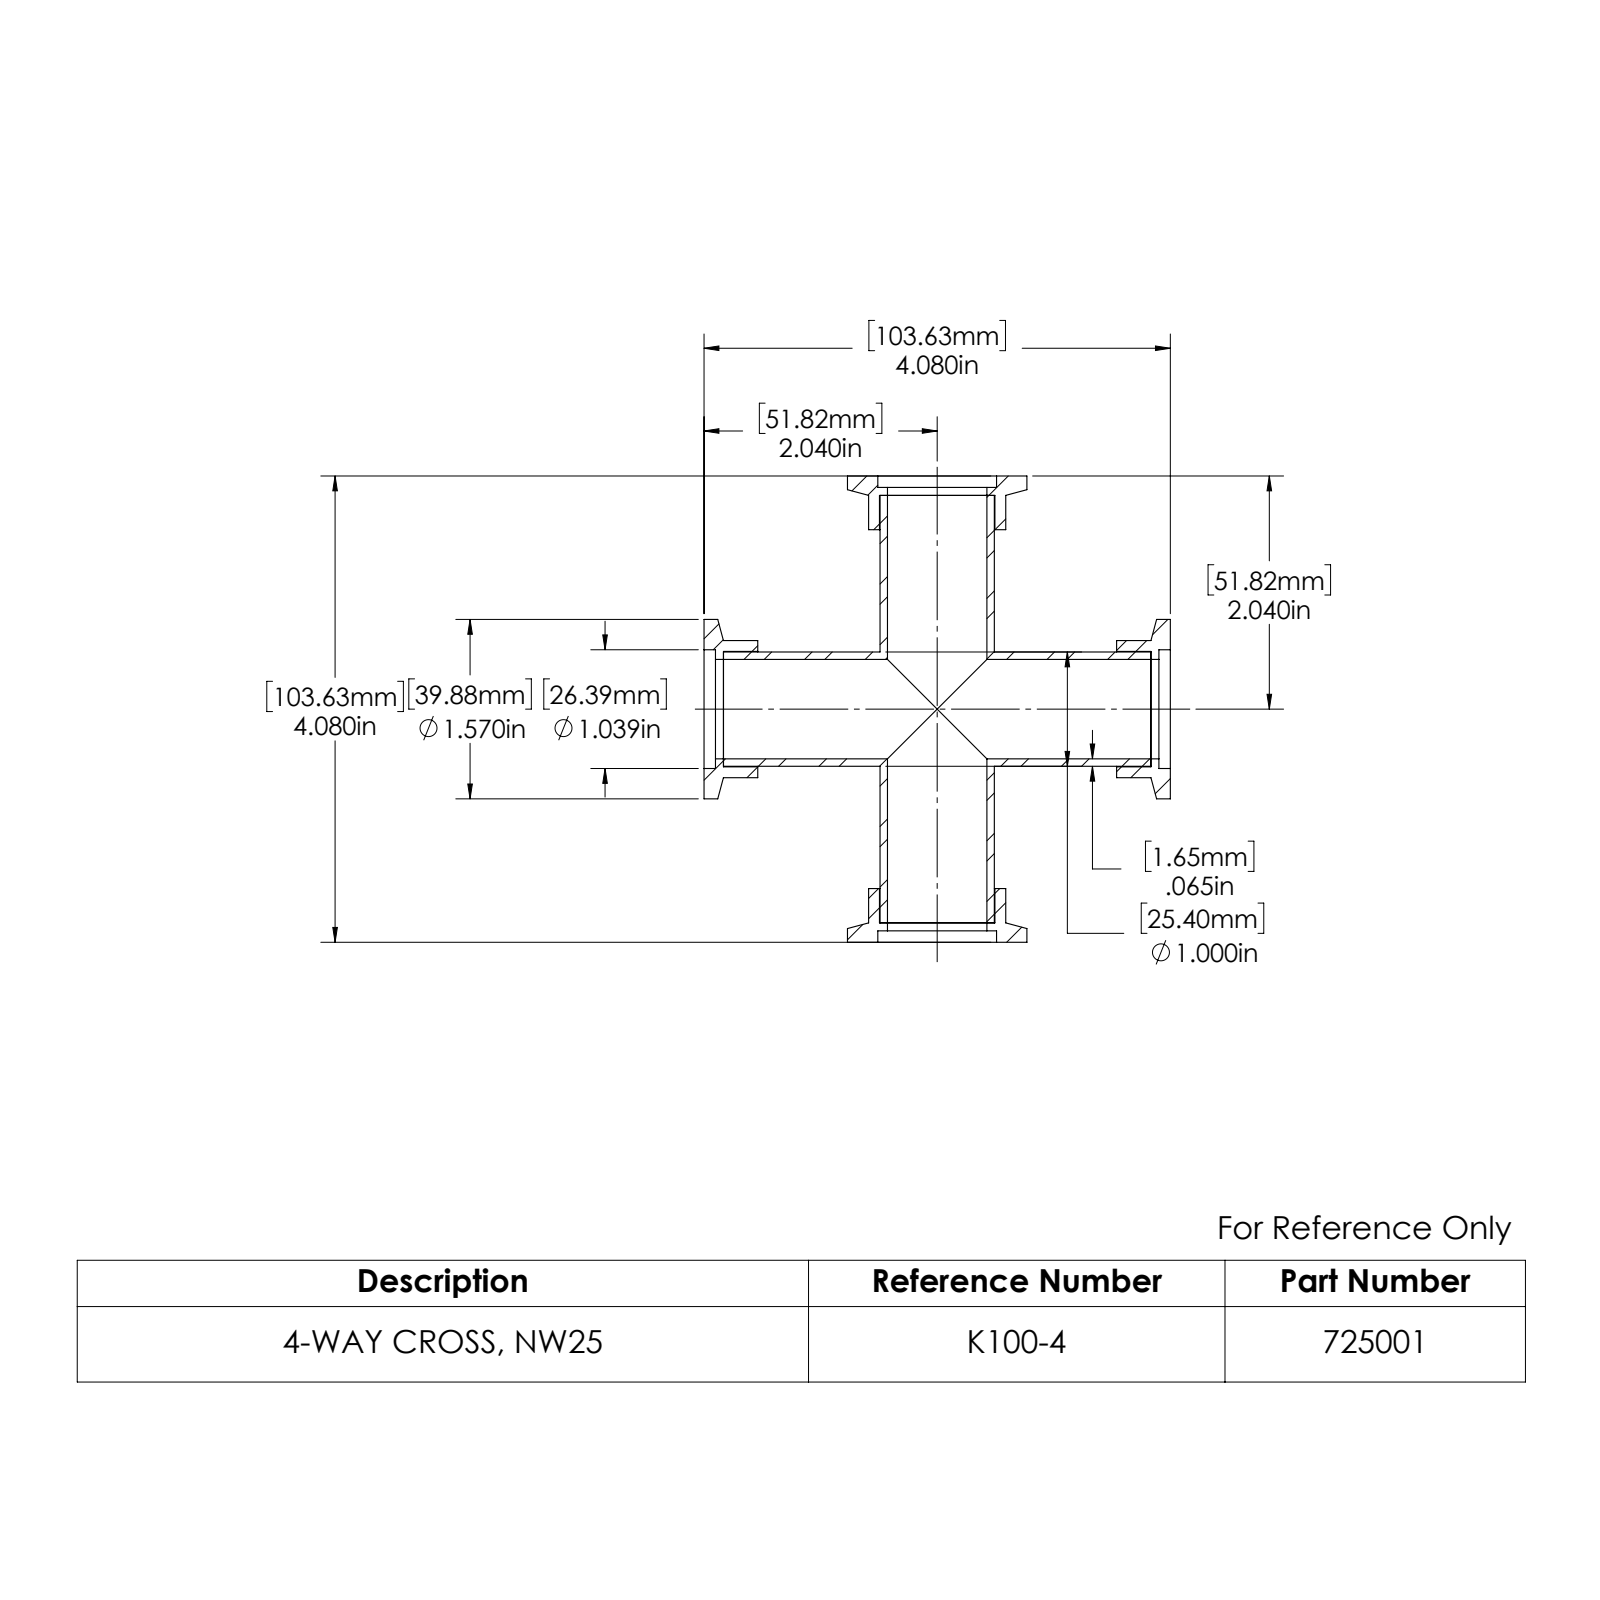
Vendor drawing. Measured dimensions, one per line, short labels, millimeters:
name: 725001; 405501; 713002
written by: SolidWorks 2022 (AUTOMOTIVE_DESIGN)
unit: mm
bodies: 5 solids, 84 faces (20 planar, 56 cylindrical, 8 other)
size: 103.6 × 103.6 × 39.9
volume: 38 050 mm³; area: 39 550 mm²
holes: 2× ⌀22.1, 2× ⌀25.7, 2× ⌀26.4
bosses: 2× ⌀39.9, 2× ⌀30.5, 2× ⌀25.4
face distances: 103.6, 7.6, 87.4, 2.5, 101.1, 4.3, 99.3, 95, 99.3, 4.3
